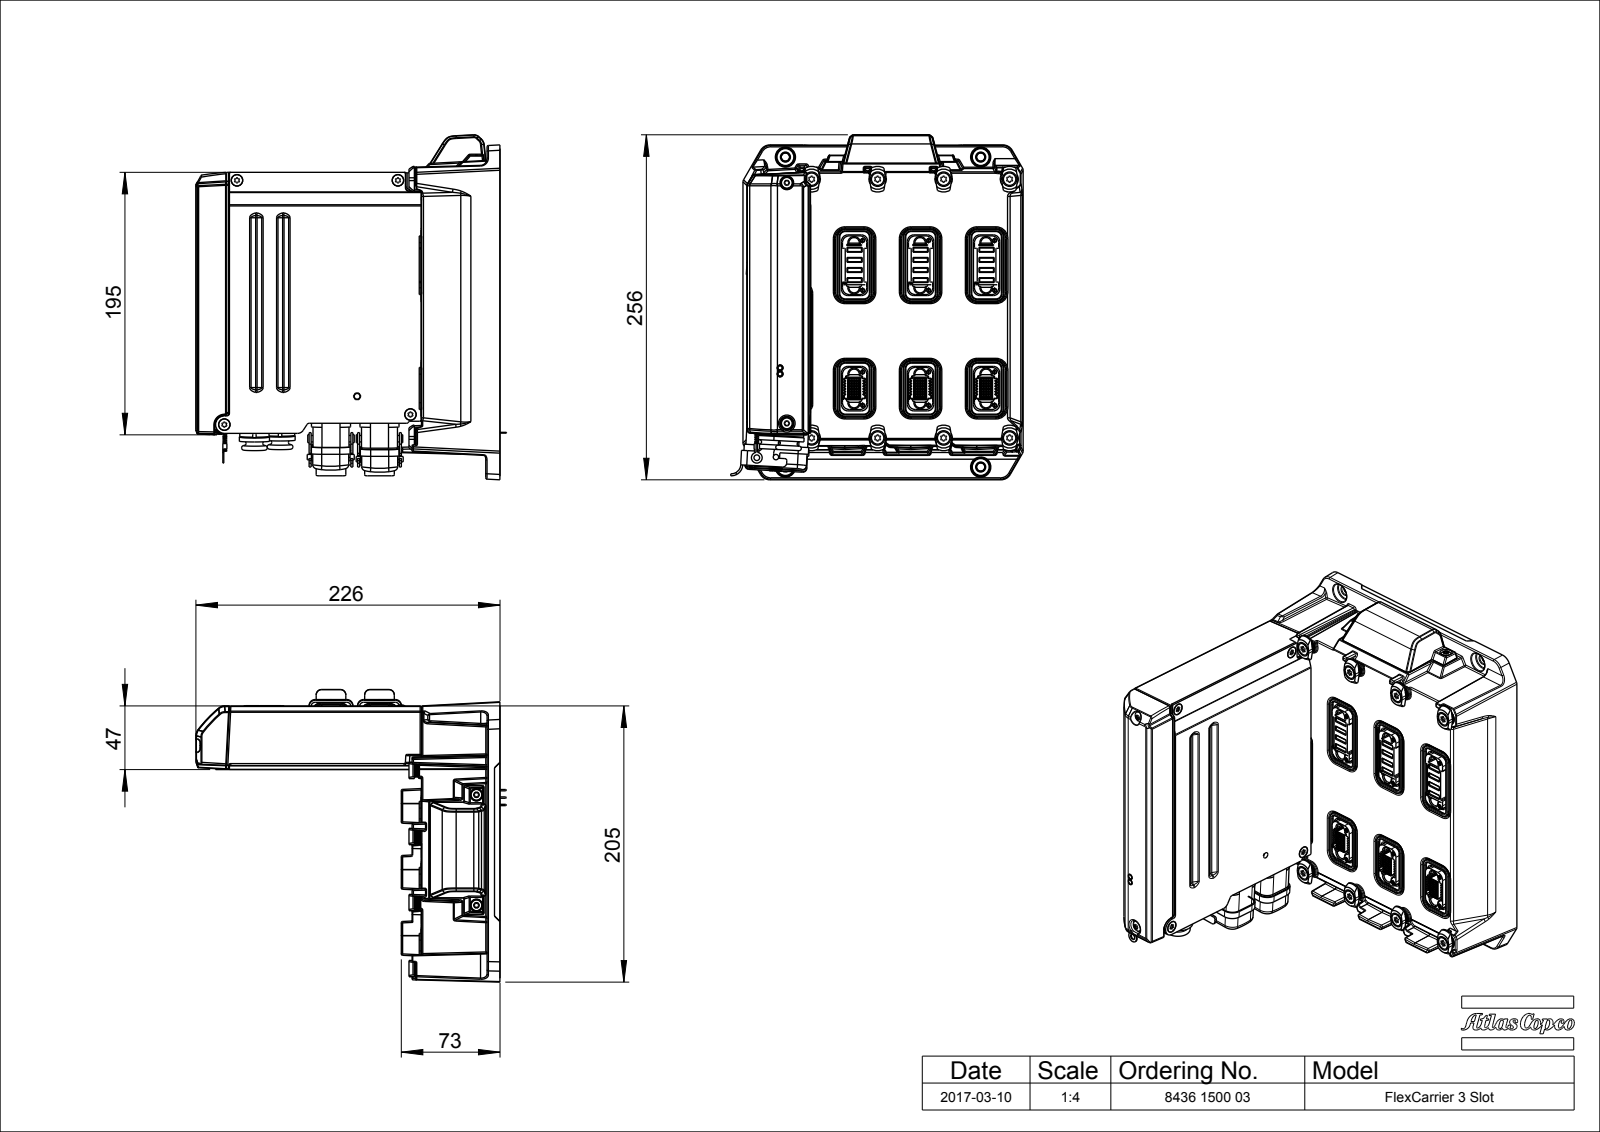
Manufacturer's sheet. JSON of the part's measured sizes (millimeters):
{"part_name": "4222190411; 0384300060; 4222191700; 0219110049 (+8 more)", "step_written_by": "CREO PARAMETRIC BY PTC INC, 2020281 (CONFIG_CONTROL_DESIGN)", "units": "millimeters", "bodies": {"solids": 75, "faces": 23625, "planar": 12603, "cylindrical": 4647, "other": 6375}, "overall_size": [256.04, 225.8, 217.13], "volume_mm3": 3427000, "surface_area_mm2": 821994, "round_holes": [[2.5, 27], [2.86, 12], [3.5, 10], [4.2, 9], [3.3, 8], [5.3, 8], [1.88, 6], [4.1, 5], [4.26, 5], [6.3, 5], [6.4, 5], [2.13, 4]], "round_bosses_or_shafts": [[0.5, 20], [4, 18], [8.4, 13], [2.72, 12], [0.5, 12], [5, 10], [9.2, 8], [6, 6]], "partial_cylinders_radius": [[0.5, 651], [1, 571], [0.13, 240], [0.4, 96], [0.7, 96], [4, 74], [0.3, 63], [3.04, 60]], "face_to_face_distances": [1.5, 2, 3.5, 3, 38.5, 37, 40.5, 54.8, 56.3, 58.3], "hole_center_spacings": [6.76, 36, 13.4, 15.91, 33.78, 29.31, 42.71, 33.77]}
